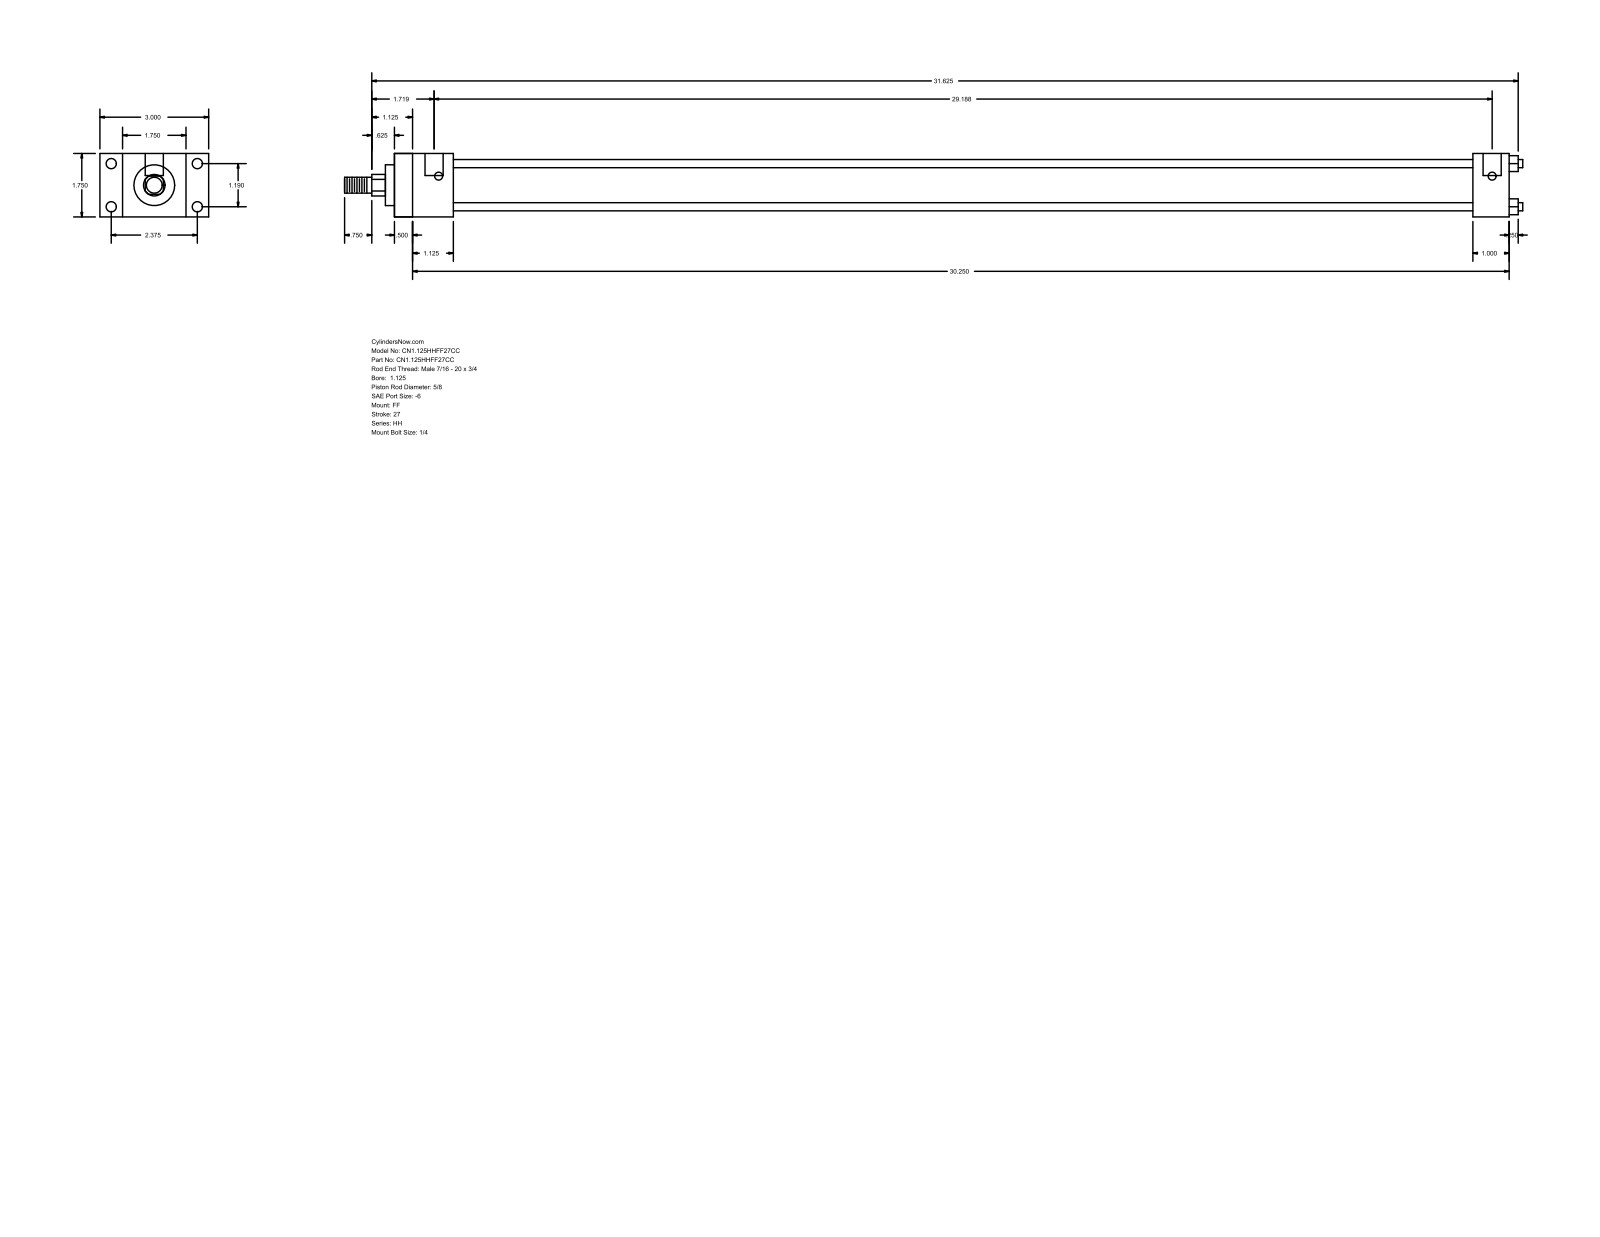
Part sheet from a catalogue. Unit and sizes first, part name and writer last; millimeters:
Units: millimetres
Overall size (bounding box): 825.5 × 76.2 × 44.45
Round holes (diameter × count): ⌀5.56 ×4, ⌀7.14 ×4, ⌀12.7 ×2
Round bosses / shafts (diameter × count): ⌀5.71 ×4, ⌀34.92 ×1, ⌀28.57 ×1, ⌀15.88 ×1, ⌀11.11 ×1
Partial cylindrical surfaces — rounded edges, fillets, slot ends (radius × count): R7.54 ×1
Main face-to-face distances: 44.46, 781.04, 12.69, 768.35, 15.87, 28.58, 60.33, 25.4, 41.27, 755.64
Hole centre spacings: 30.22, 60.32, 67.47, 738.19, 3.17, 741.36
Bodies: 0 solids, 92 faces (64 planar, 28 cylindrical, 0 other)
Part name (STEP PRODUCT): HH_FF__0112_0.625
STEP written by: GSSL Pune (CONFIG_CONTROL_DESIGN)
